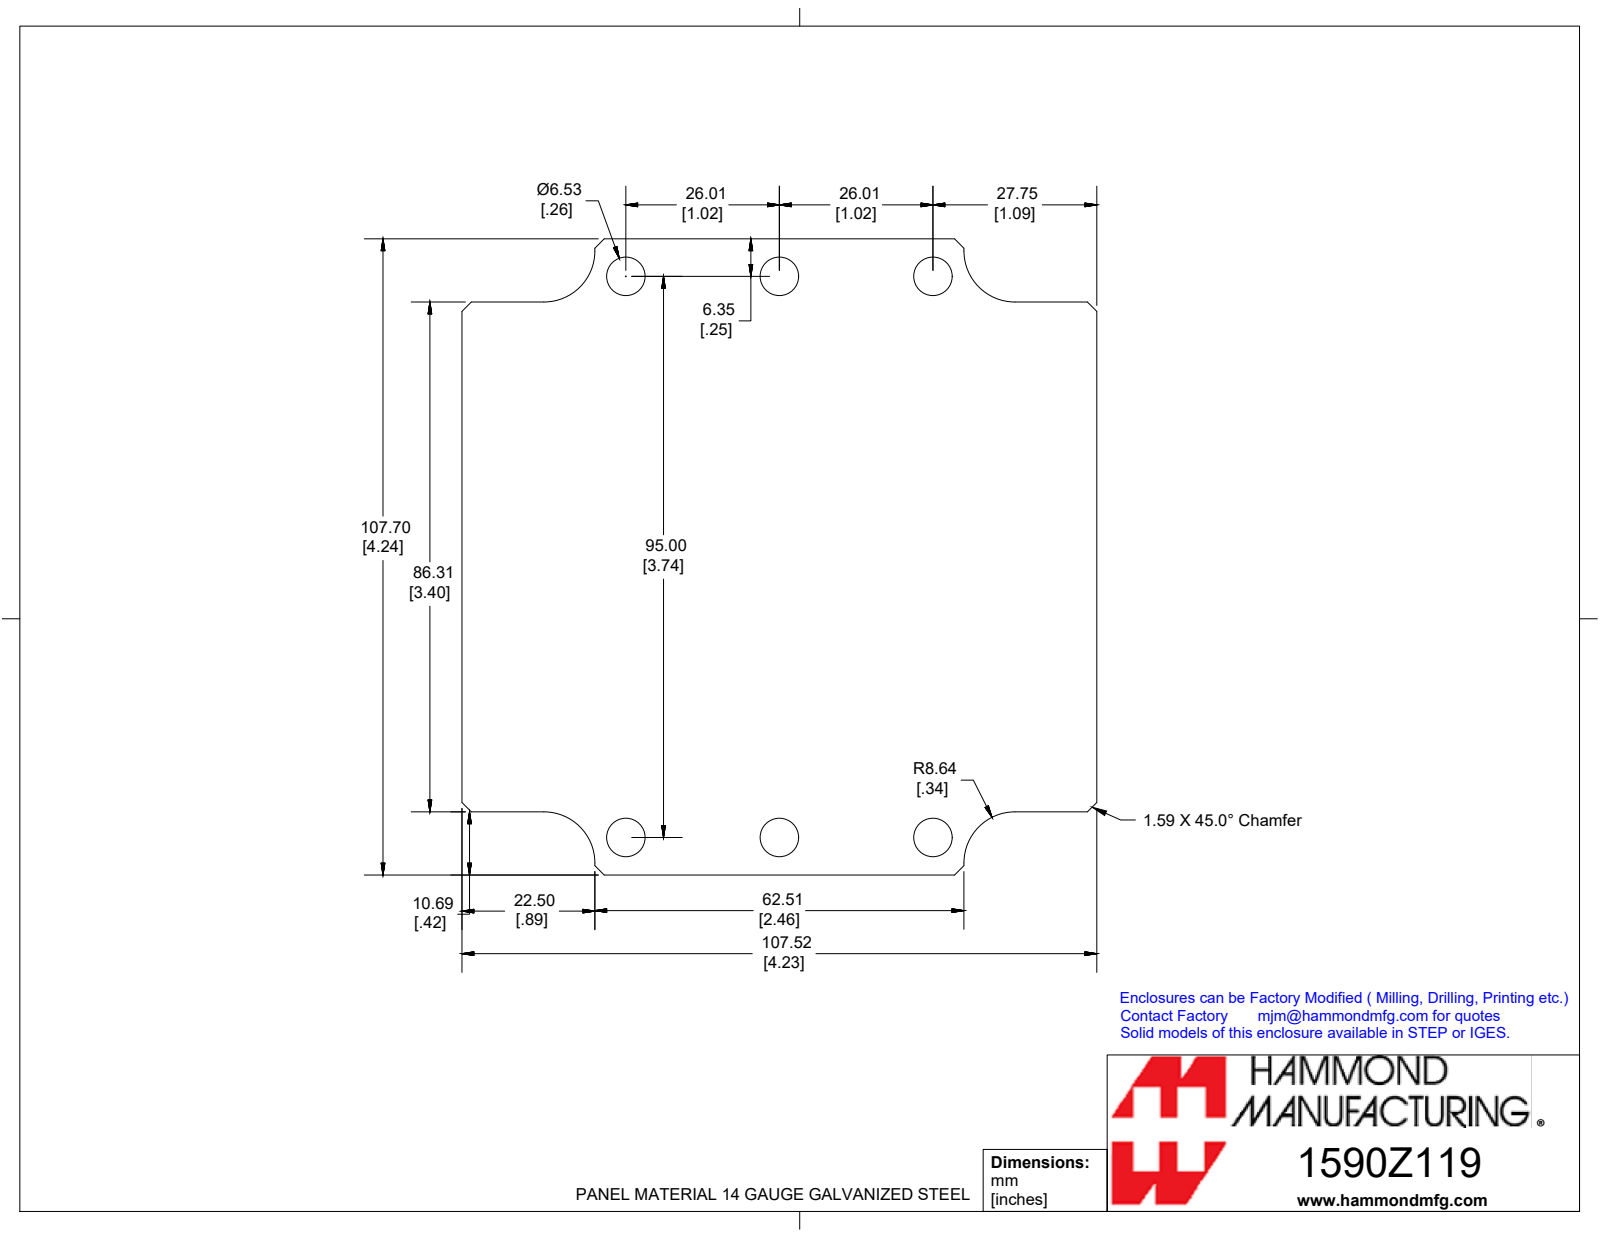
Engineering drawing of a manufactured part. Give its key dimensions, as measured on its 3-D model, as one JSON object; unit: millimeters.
{"part_name": "1590Z119PL", "step_written_by": "SolidWorks 2019 (CONFIG_CONTROL_DESIGN)", "units": "millimeters", "bodies": {"solids": 1, "faces": 32, "planar": 22, "cylindrical": 10, "other": 0}, "overall_size": [107.7, 107.5, 1.6], "volume_mm3": 16880, "surface_area_mm2": 21790, "round_holes": [[6.5, 6]], "partial_cylinders_radius": [[8.6, 4]], "face_to_face_distances": [1.6, 107.5, 107.7, 10.7, 97, 86.3, 8.4, 126.4, 118.1, 134.8], "hole_center_spacings": [26, 99.5, 96, 52, 109.2]}
